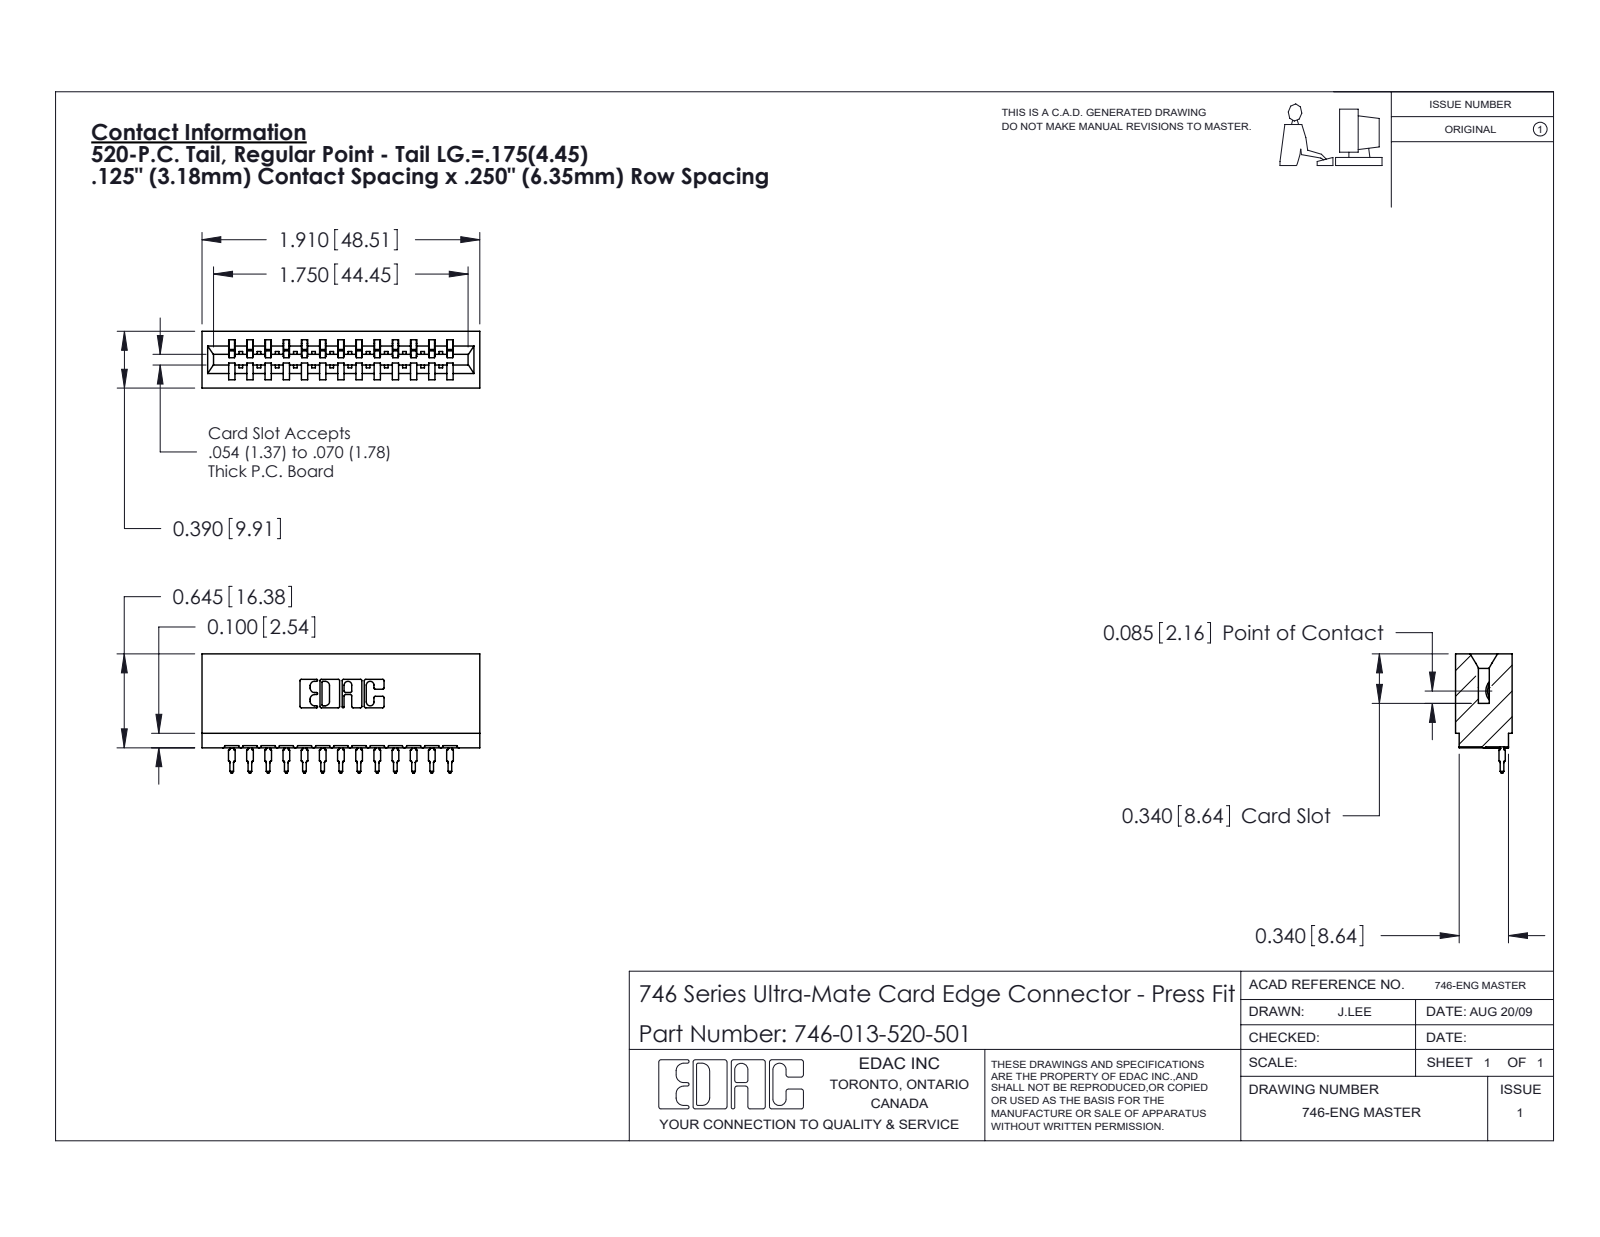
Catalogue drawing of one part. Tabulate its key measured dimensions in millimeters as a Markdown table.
| quantity | value |
| --- | --- |
| part name | 746-013-520-501; 746 Part_.340 Slot Depth - 01; 746-292-001_520 |
| STEP written by | SolidWorks 2020 (CONFIG_CONTROL_DESIGN) |
| units | millimeters |
| bodies | 14 solids, 1501 faces (874 planar, 289 cylindrical, 338 other) |
| overall size | 48.5 × 20.8 × 9.9 |
| volume | 5 600 mm³ |
| surface area | 7 019 mm² |
| partial cylindrical surfaces (radius × count) | 0.5 × 26, 0.3 × 22, 0.4 × 14, 0.2 × 6, 0.8 × 6, 0.1 × 4, 0.3 × 4, 0.7 × 3 |
| main face-to-face distances | 6.4, 12.7, 8.5, 1.4, 3.2, 9.9, 1.1, 7.4, 19.1, 3.2 |
